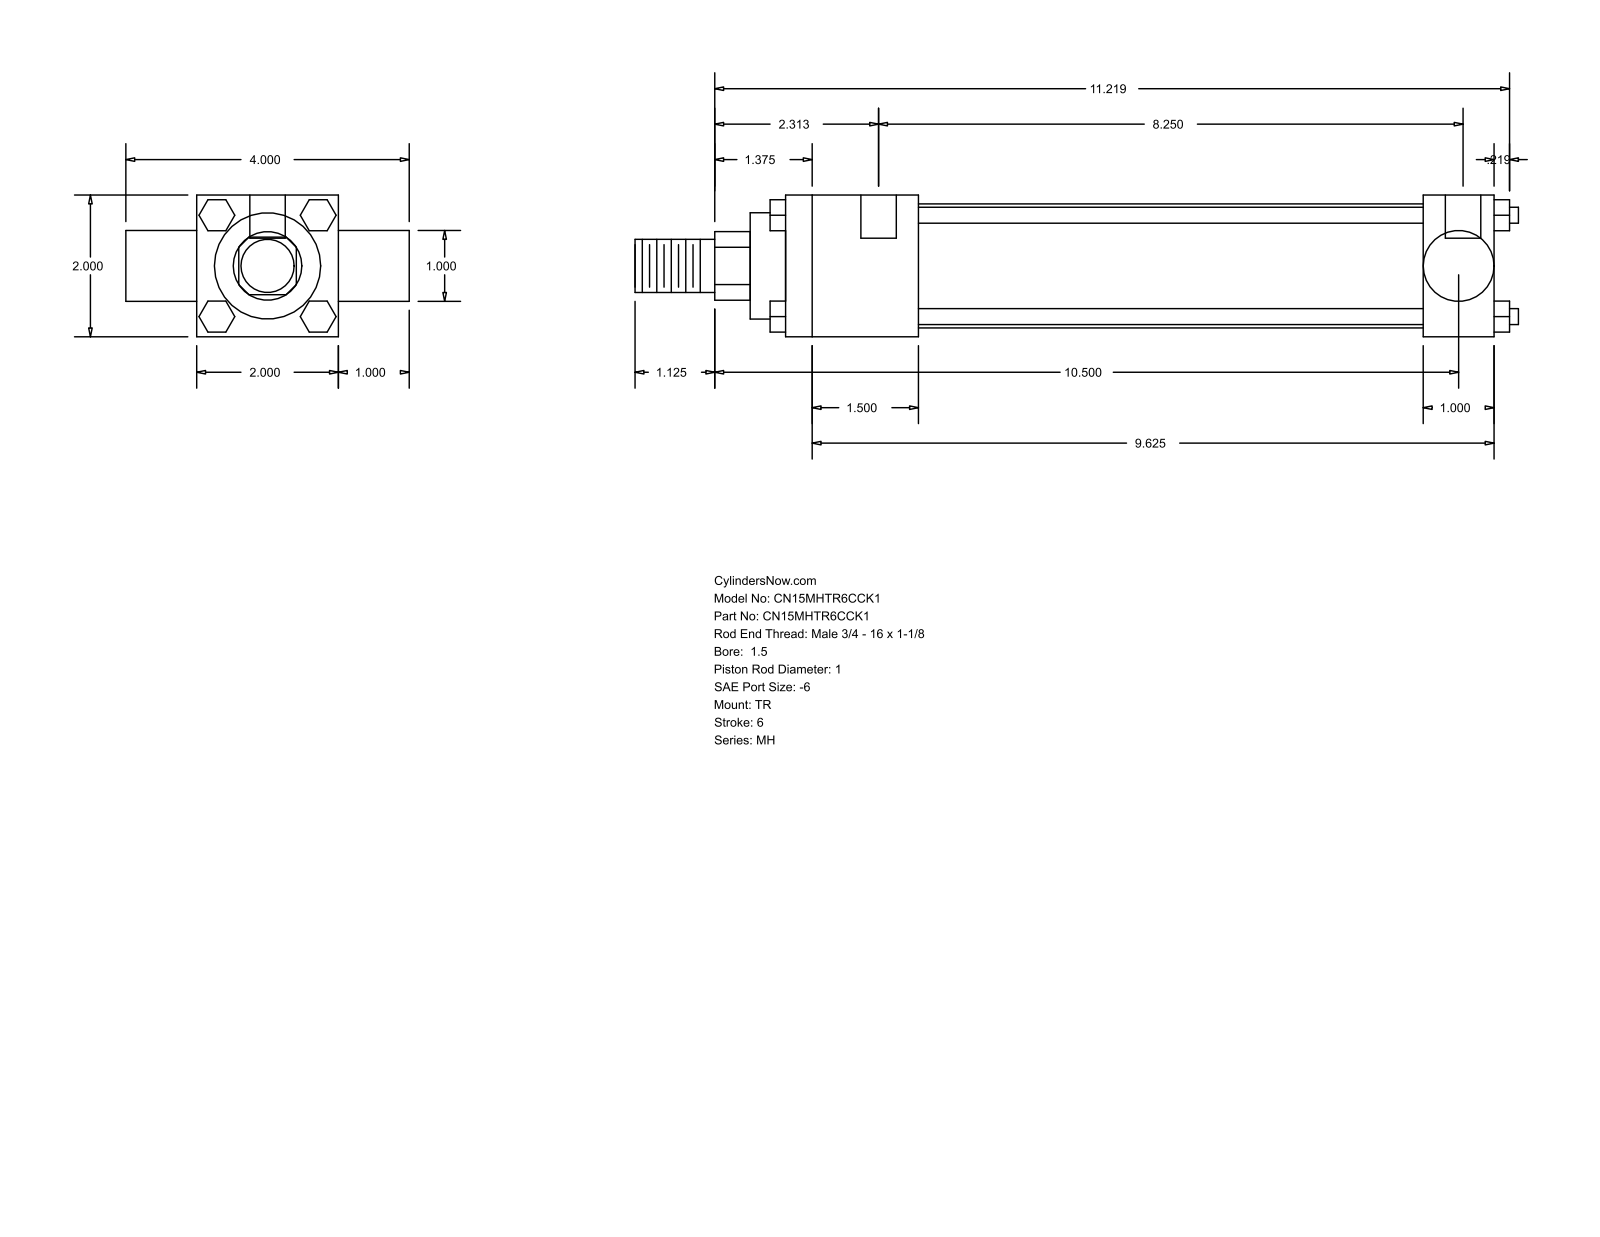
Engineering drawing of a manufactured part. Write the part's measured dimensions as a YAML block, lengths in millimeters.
part_name: "MH_TR__0150_1"
step_written_by: "GSSL Pune (CONFIG_CONTROL_DESIGN)"
units: millimeters
bodies: {solids: 0, faces: 120, planar: 92, cylindrical: 28, other: 0}
overall_size: [316.71, 101.6, 50.8]
round_holes:
  - {diameter: 5.56, count: 3}
  - {diameter: 12.7, count: 2}
round_bosses_or_shafts:
  - {diameter: 5.71, count: 4}
  - {diameter: 44.45, count: 1}
  - {diameter: 38.1, count: 1}
  - {diameter: 25.4, count: 1}
  - {diameter: 25.35, count: 1}
  - {diameter: 19.05, count: 1}
partial_cylinders:
  - {radius: 12.29, count: 1}
face_to_face_distances: [50.8, 25.4, 254, 76.2, 47.63, 206.37, 228.6, 180.97, 101.6, 12.7]
hole_center_spacings: [3.18, 209.55, 212.73]
